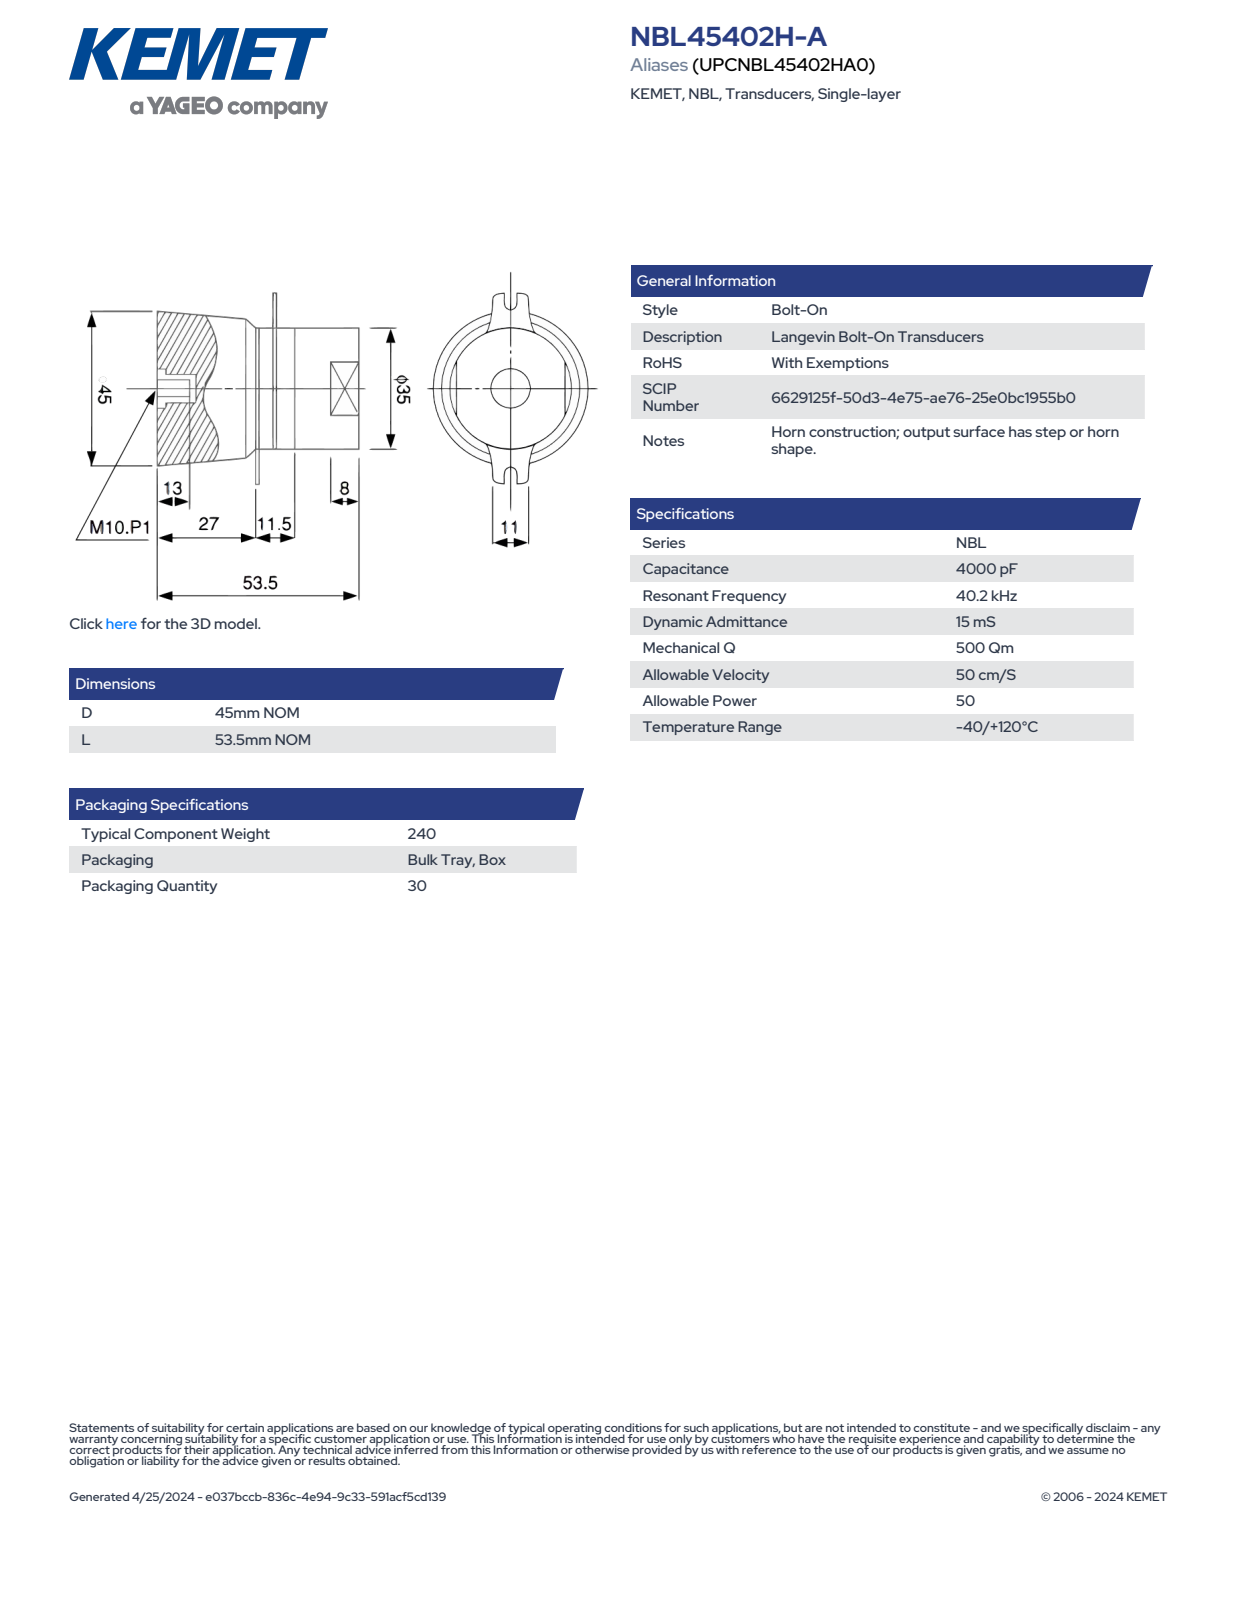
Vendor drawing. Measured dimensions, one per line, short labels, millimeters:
name: ATB_45402HA_D45L53.5
written by: SolidWorks 2014 (AUTOMOTIVE_DESIGN)
unit: mm
bodies: 1 solid, 100 faces (26 planar, 14 cylindrical, 60 other)
size: 56.09 × 53.5 × 45
volume: 60 285 mm³; area: 11 767 mm²
holes: 1× ⌀10
bosses: 1× ⌀35, 1× ⌀34.5
rounds: 2× R1.62, 1× R15.42, 1× R15.85
face distances: 32.7, 32.8, 53.5, 20.8, 20.7, 0.5, 5.45, 5.7, 5.8, 30.78
